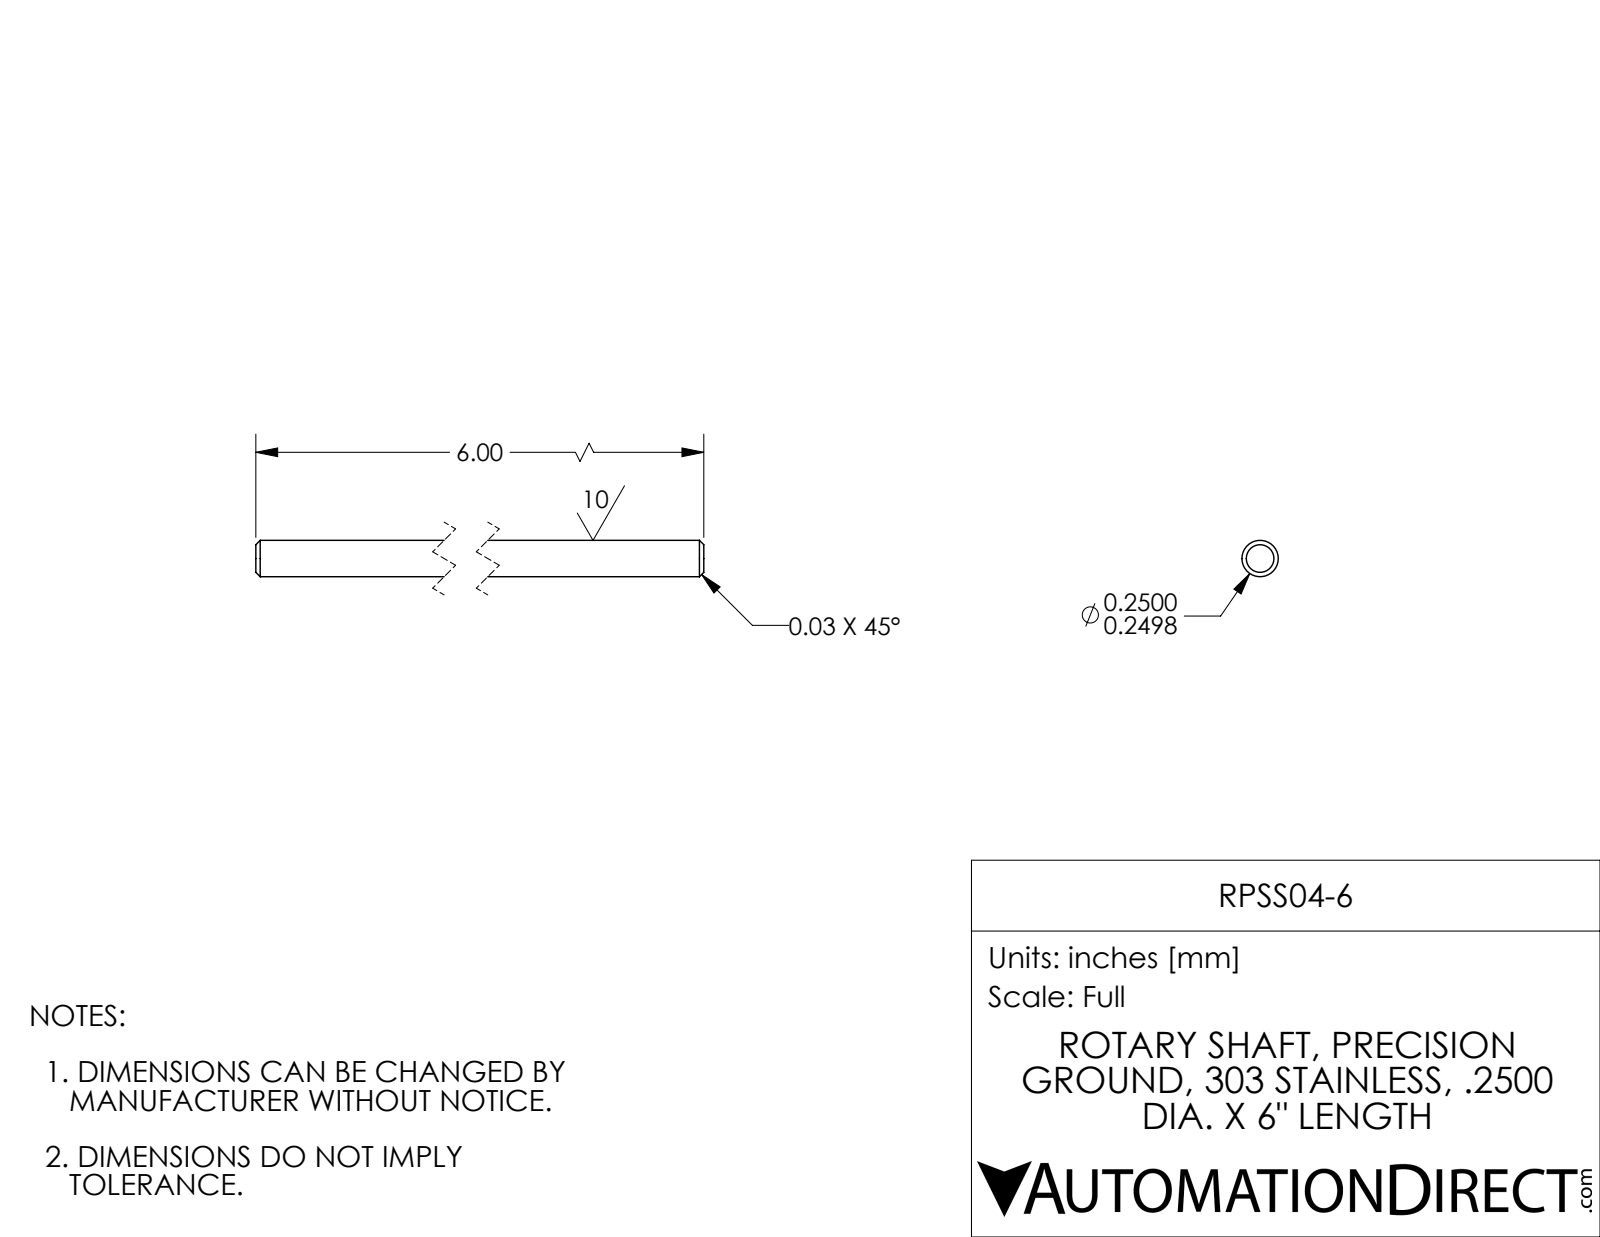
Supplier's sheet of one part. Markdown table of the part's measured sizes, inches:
| quantity | value |
| --- | --- |
| part name | RPSS04-6 |
| STEP written by | SolidWorks 2017 (AUTOMOTIVE_DESIGN) |
| units | inches |
| bodies | 1 solid, 8 faces (2 planar, 2 cylindrical, 4 other) |
| overall size | 6 × 0.25 × 0.25 |
| volume | 0.294 in³ |
| surface area | 4.781 in² |
| round bosses / shafts (diameter × count) | 0.25 × 1 |
| main face-to-face distances | 6 |
